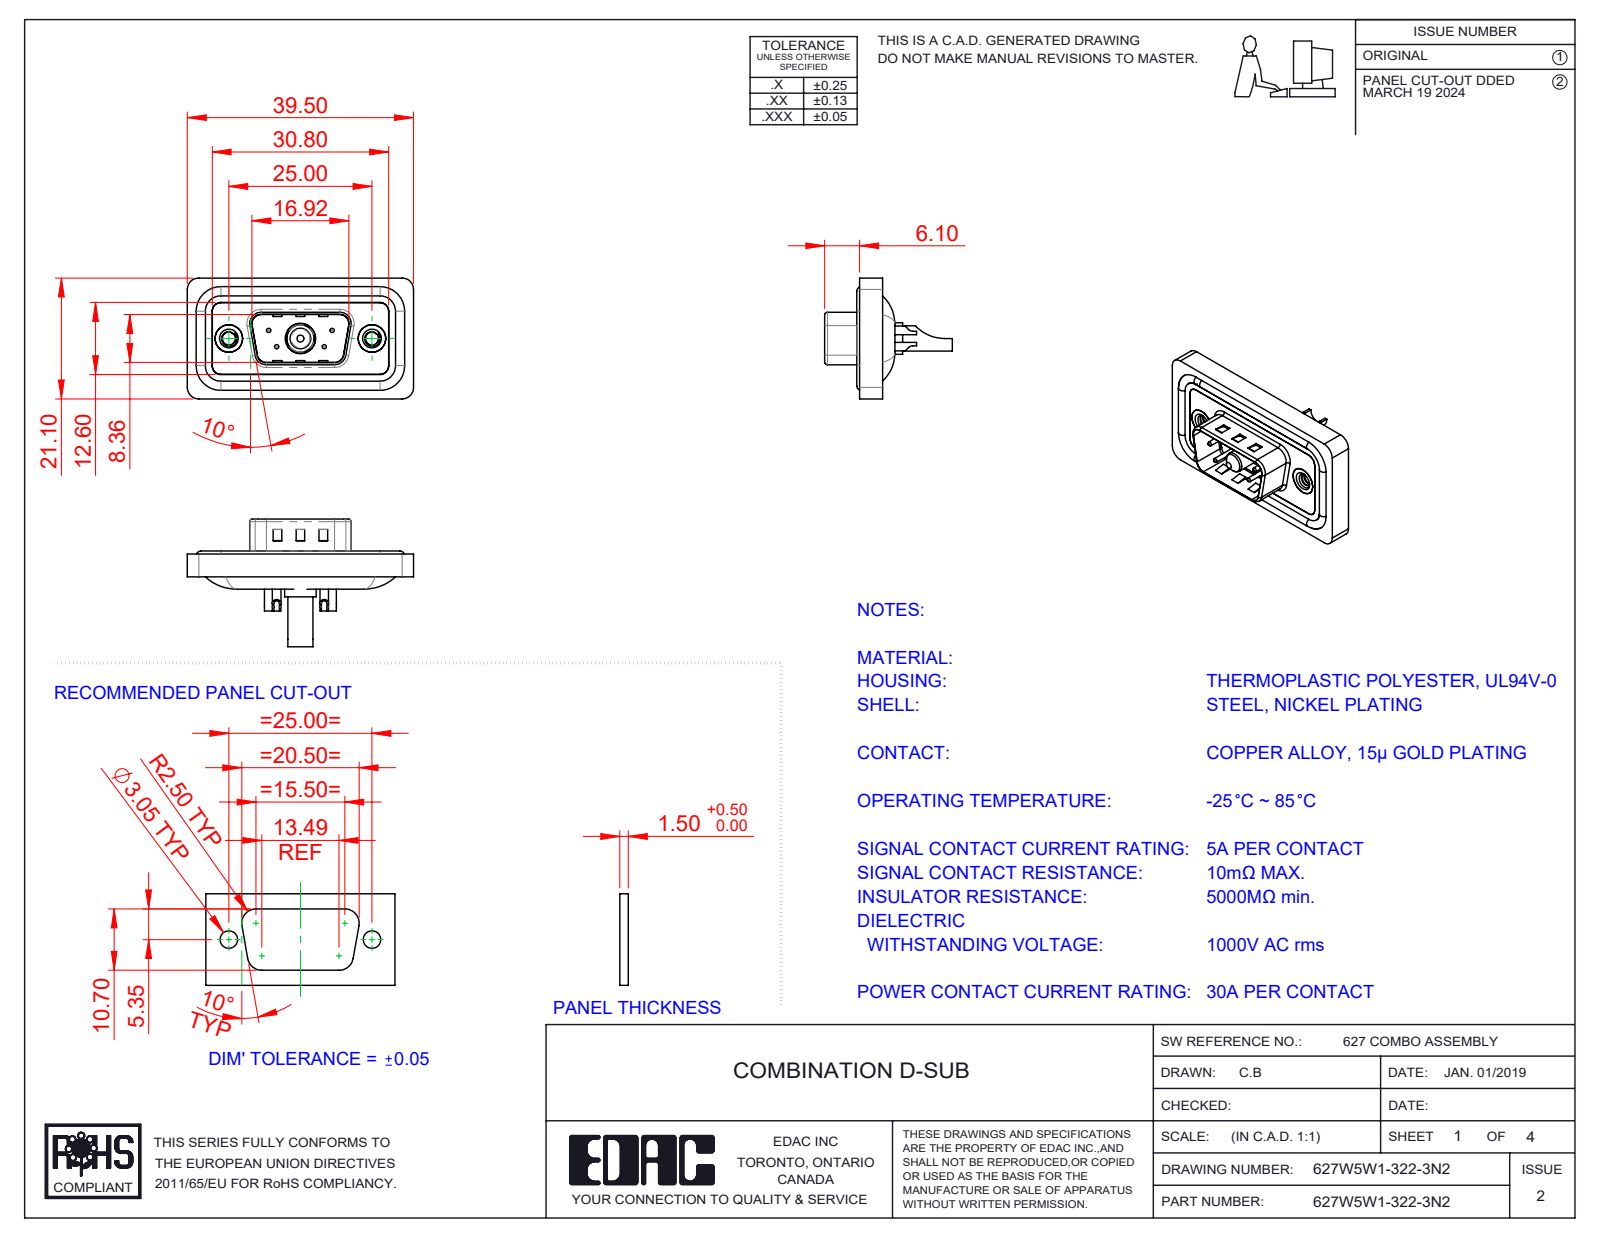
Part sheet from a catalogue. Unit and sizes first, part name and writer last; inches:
Units: inches
Overall size (bounding box): 1.555 × 0.878 × 0.831
Round holes (diameter × count): ⌀0.03 ×4, ⌀0.039 ×4, ⌀0.063 ×4, ⌀0.079 ×4, ⌀0.089 ×2, ⌀0.157 ×2, ⌀0.189 ×2, ⌀0.197 ×2, ⌀0.138 ×1, ⌀0.191 ×1, ⌀0.209 ×1
Round bosses / shafts (diameter × count): ⌀0.063 ×4, ⌀0.059 ×4, ⌀0.193 ×2, ⌀0.217 ×1, ⌀0.205 ×1, ⌀0.187 ×1, ⌀0.173 ×1, ⌀0.148 ×1
Partial cylindrical surfaces — rounded edges, fillets, slot ends (radius × count): R0.059 ×22, R0.079 ×18, R0.02 ×8, R0.063 ×8, R0.039 ×6, R0.01 ×4, R0.024 ×4, R0.026 ×4
Main face-to-face distances: 0.016, 0.043, 0.114, 0.063, 0.122, 0.02, 0.059, 0.098, 0.157, 0.031
Hole centre spacings: 0.124, 0.225, 0.28, 0.492, 0.713, 0.173, 0.173, 0.327
Volume: 0.27 in³ · Surface area: 10.98 in²
Bodies: 13 solids, 604 faces (194 planar, 266 cylindrical, 144 other)
Part name (STEP PRODUCT): 627Combo Shell Rear_09 Contacts; 627Combo Shell Front_09 Contacts; 627Combo Contact Row 1_22; 627Combo Threaded Rivet_2 (+5 more)
STEP written by: SolidWorks 2023 (CONFIG_CONTROL_DESIGN)
